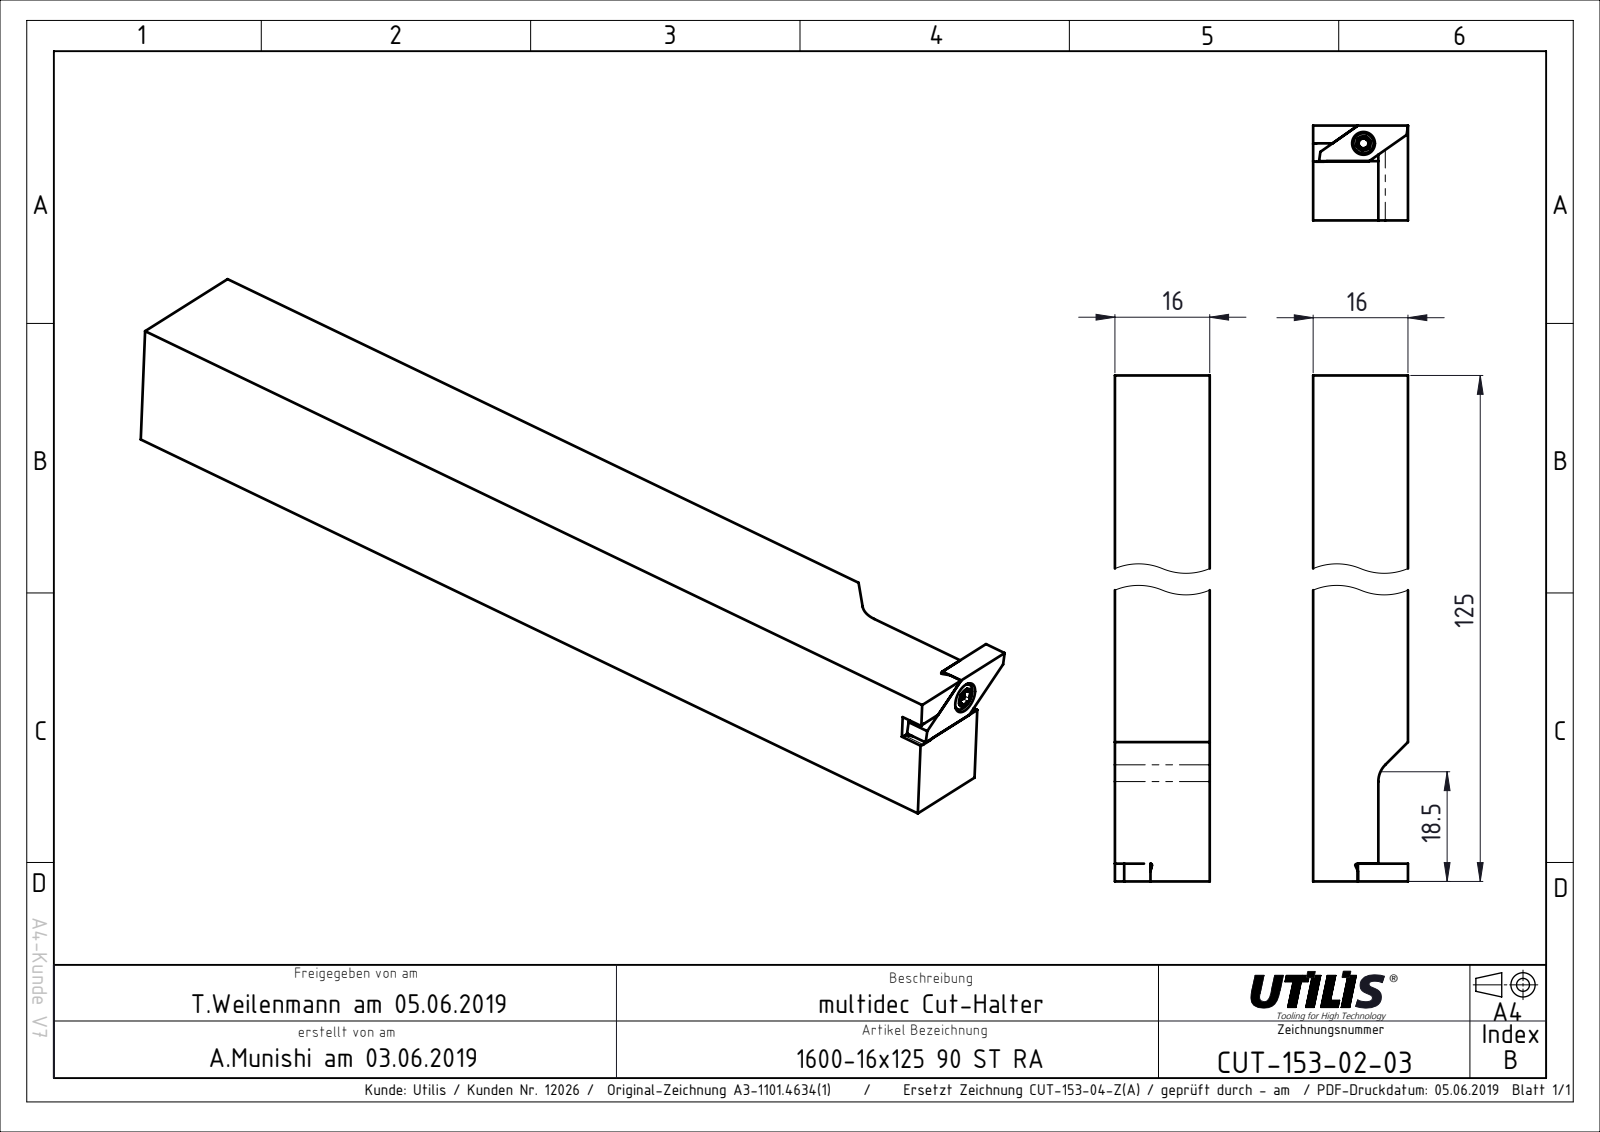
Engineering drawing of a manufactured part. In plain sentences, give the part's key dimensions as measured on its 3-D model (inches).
The part is named "CUT-153-02-03". Its 3-D file was written by "SolidWorks 2018 (AUTOMOTIVE_DESIGN)". It is 1 solid with 12 faces: 11 planar, 1 cylindrical and 0 other. Overall it measures 4.921 by 0.63 by 0.63 inches. Its volume is 1.853 cubic inches and its surface area 12.88 square inches. Partial cylindrical surfaces (rounded edges, fillets, slot ends): 1 of radius 0.157. The main face-to-face distances are 0.63, 0.197, 0.433, 4.921, 0.118, 4.803.
